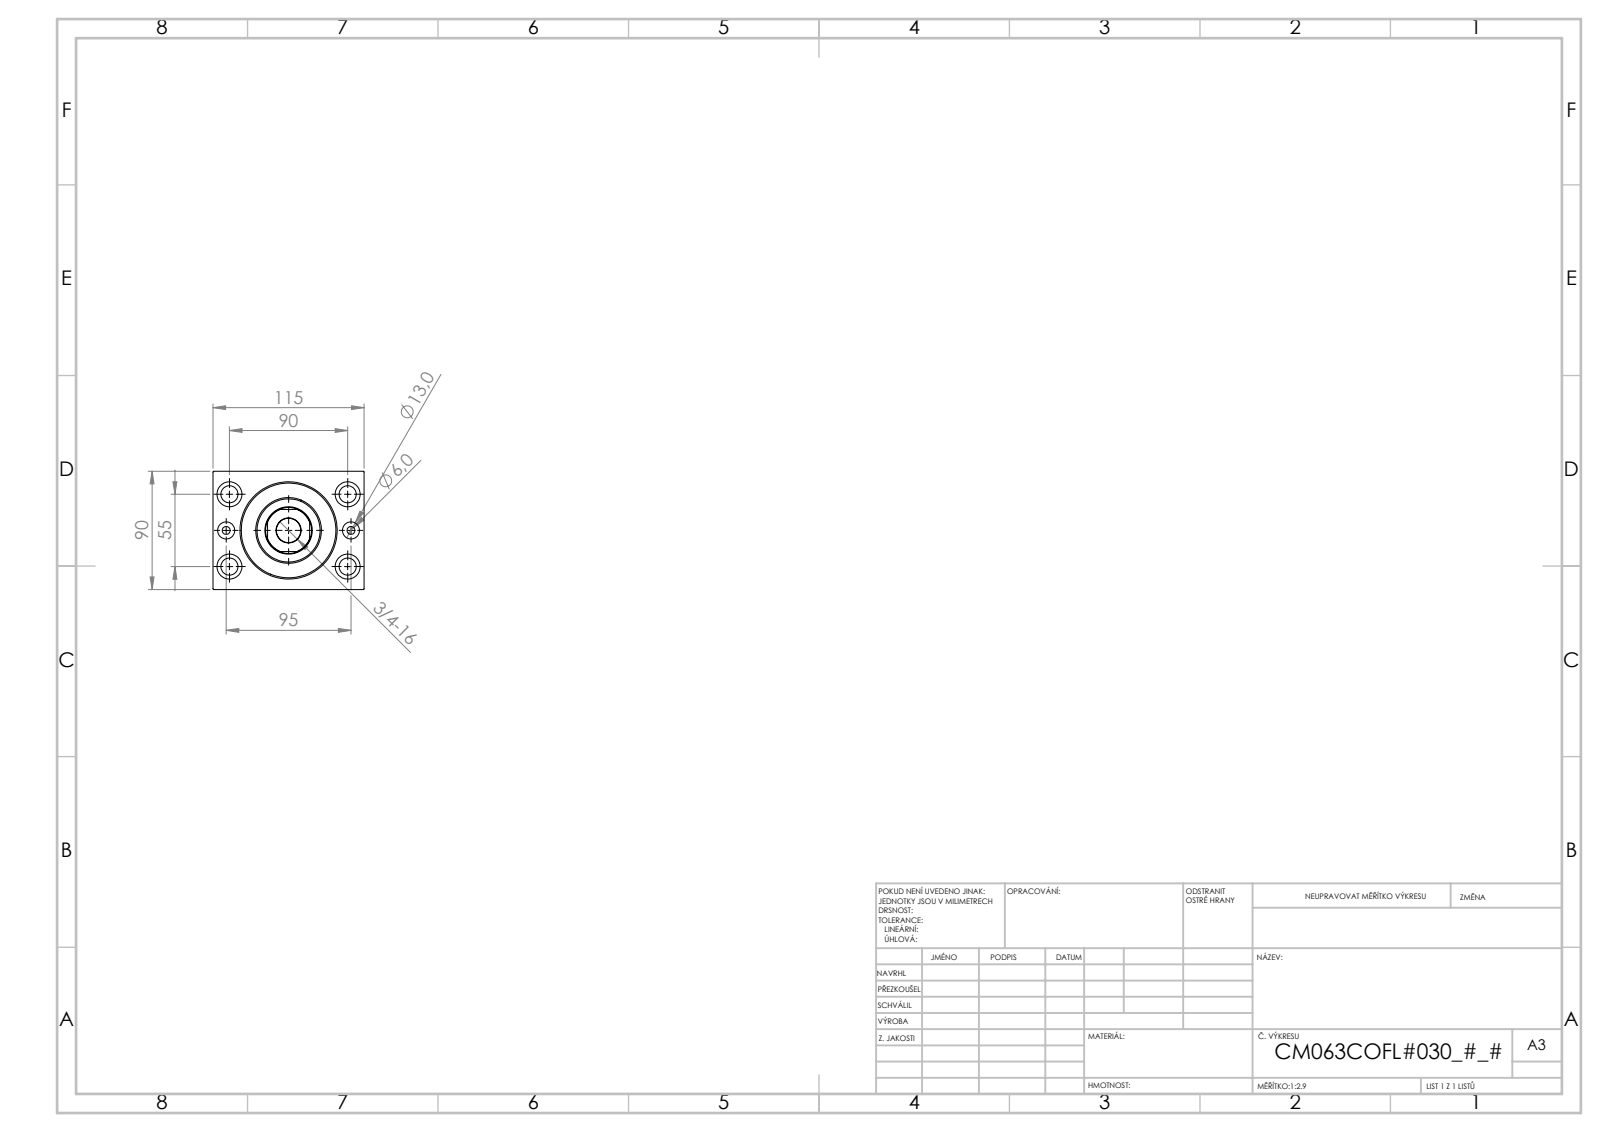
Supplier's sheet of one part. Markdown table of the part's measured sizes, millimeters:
| quantity | value |
| --- | --- |
| part name | V450CM_C_VCP; V450CM_VC_B; V450CM_C_Body |
| STEP written by | SolidWorks 2019 (CONFIG_CONTROL_DESIGN) |
| units | millimeters |
| bodies | 3 solids, 858 faces (408 planar, 56 cylindrical, 394 other) |
| overall size | 121.5 × 115 × 90 |
| volume | 982 871 mm³ |
| surface area | 139 984 mm² |
| round holes (diameter × count) | 13 × 6, 19 × 4, 6 × 2, 18.5 × 1, 36 × 1, 63 × 1, 65 × 1, 72 × 1 |
| round bosses / shafts (diameter × count) | 50 × 1 |
| partial cylindrical surfaces (radius × count) | 17.5 × 1 |
| main face-to-face distances | 90, 115, 108, 17.5, 90.5, 13.5, 77, 94.5, 43.5, 30 |
| hole center spacings | 27.61, 52.74, 96.5, 47.5, 55, 90, 105.48, 95 |
